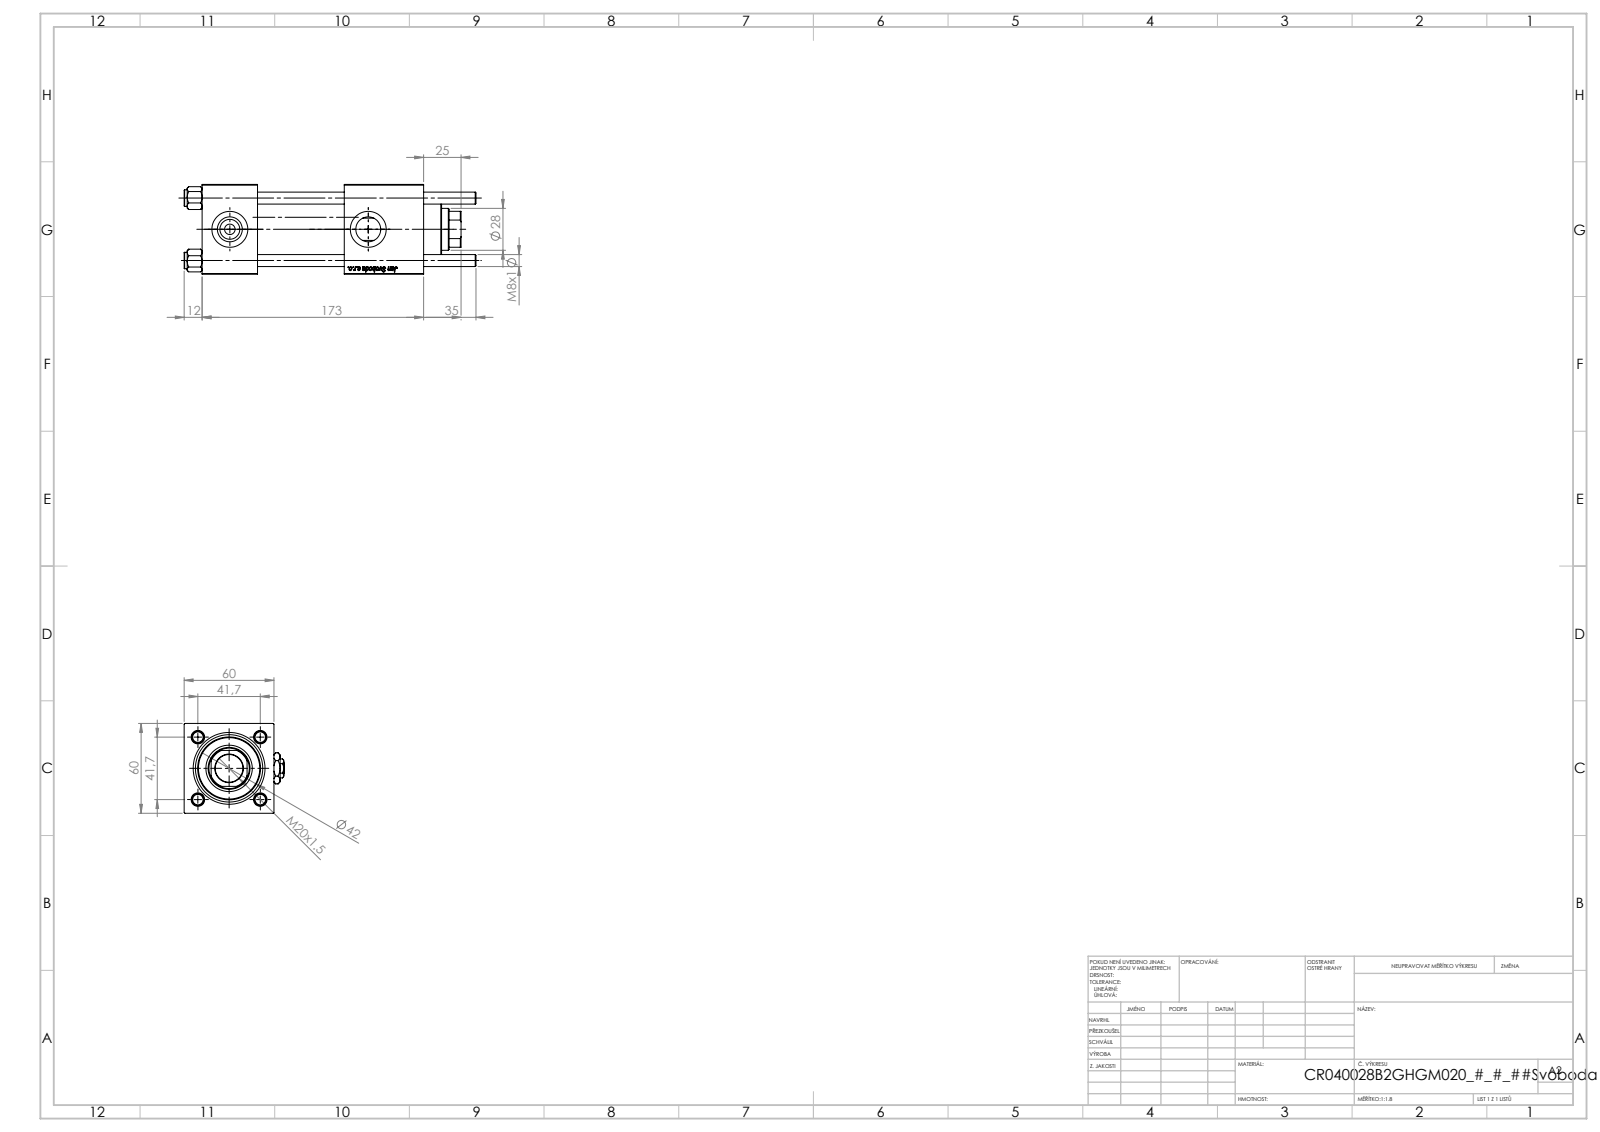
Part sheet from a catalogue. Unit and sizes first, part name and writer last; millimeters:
Units: millimetres
Overall size (bounding box): 195 × 67 × 60
Round holes (diameter × count): ⌀8 ×4, ⌀7 ×2, ⌀16.66 ×2, ⌀24 ×2, ⌀18.5 ×1, ⌀28 ×1, ⌀31 ×1, ⌀40 ×1, ⌀45 ×1
Round bosses / shafts (diameter × count): ⌀11 ×4, ⌀46 ×1, ⌀42 ×1
Partial cylindrical surfaces — rounded edges, fillets, slot ends (radius × count): R13.5 ×1
Main face-to-face distances: 60, 37, 58, 95, 119.3, 82.3, 24.3, 53, 148, 111
Hole centre spacings: 29.49, 41.7, 58.97, 92.5
Volume: 434 218 mm³ · Surface area: 121 508 mm²
Bodies: 12 solids, 1211 faces (457 planar, 84 cylindrical, 670 other)
Part name (STEP PRODUCT): V215CR_B-1; V215_VC_A; NUT_M5_B; V215CR_VCP_B (+2 more)
STEP written by: SolidWorks 2019 (CONFIG_CONTROL_DESIGN)
